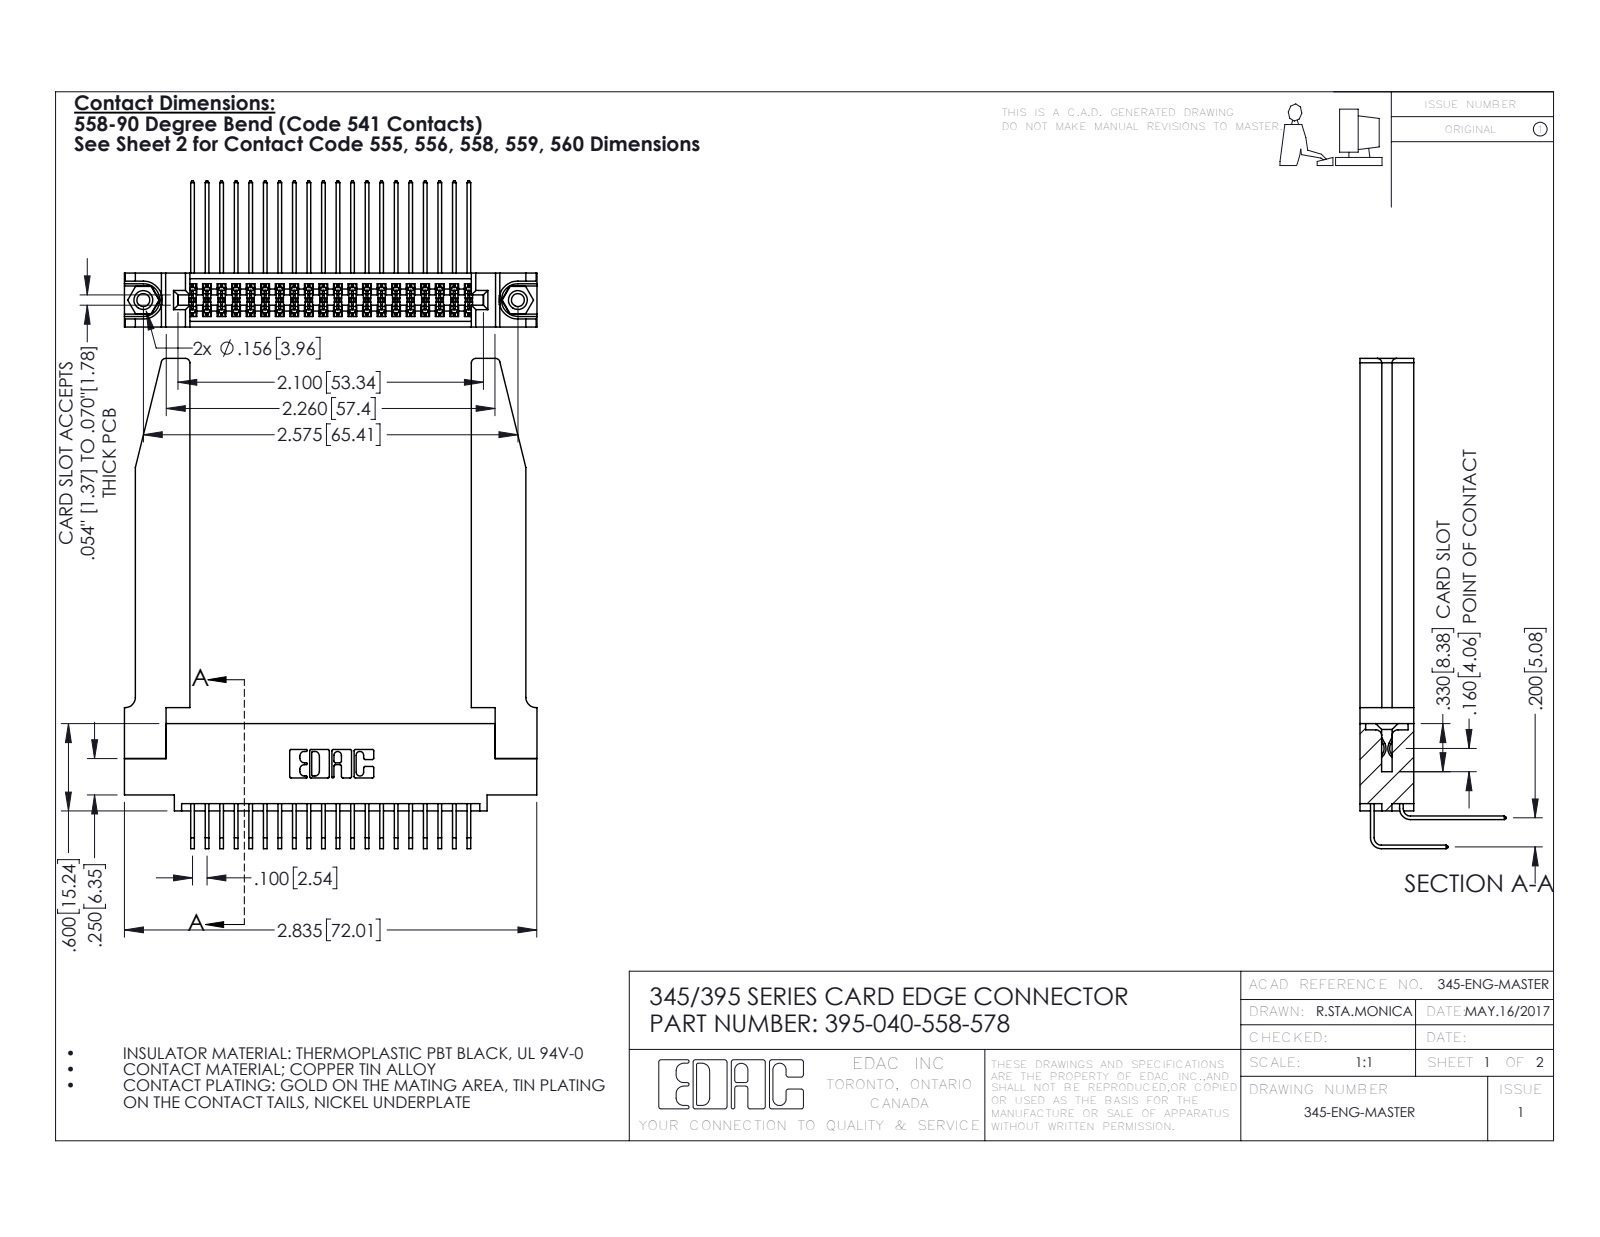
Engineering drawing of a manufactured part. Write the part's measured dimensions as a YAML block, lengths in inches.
part_name: "345-292-001_558 559 Tail - 1; 345 Part_0.110 Offset - 0.156 Dia-TH; 395-040-558-578; 345-292-001_558 Tail - 2 (+2 more)"
step_written_by: "SolidWorks 2016 (CONFIG_CONTROL_DESIGN)"
units: inches
bodies: {solids: 45, faces: 2444, planar: 1626, cylindrical: 766, other: 52}
overall_size: [3.369, 2.836, 1.005]
volume: 0.898
surface_area: 27.69
round_holes:
  - {diameter: 0.089, count: 2}
  - {diameter: 0.125, count: 2}
  - {diameter: 0.156, count: 2}
  - {diameter: 0.064, count: 1}
round_bosses_or_shafts:
  - {diameter: 0.155, count: 2}
partial_cylinders:
  - {radius: 0.006, count: 61}
  - {radius: 0.01, count: 22}
  - {radius: 0.03, count: 8}
  - {radius: 0.007, count: 6}
  - {radius: 0.031, count: 6}
  - {radius: 0.026, count: 3}
  - {radius: 0.014, count: 2}
  - {radius: 0.019, count: 2}
face_to_face_distances: [0.37, 0.072, 0.298, 0.2, 0.098, 0.272, 0.025, 0.148, 0.15, 0.225]
hole_center_spacings: [0.27, 2.341, 2.575]
